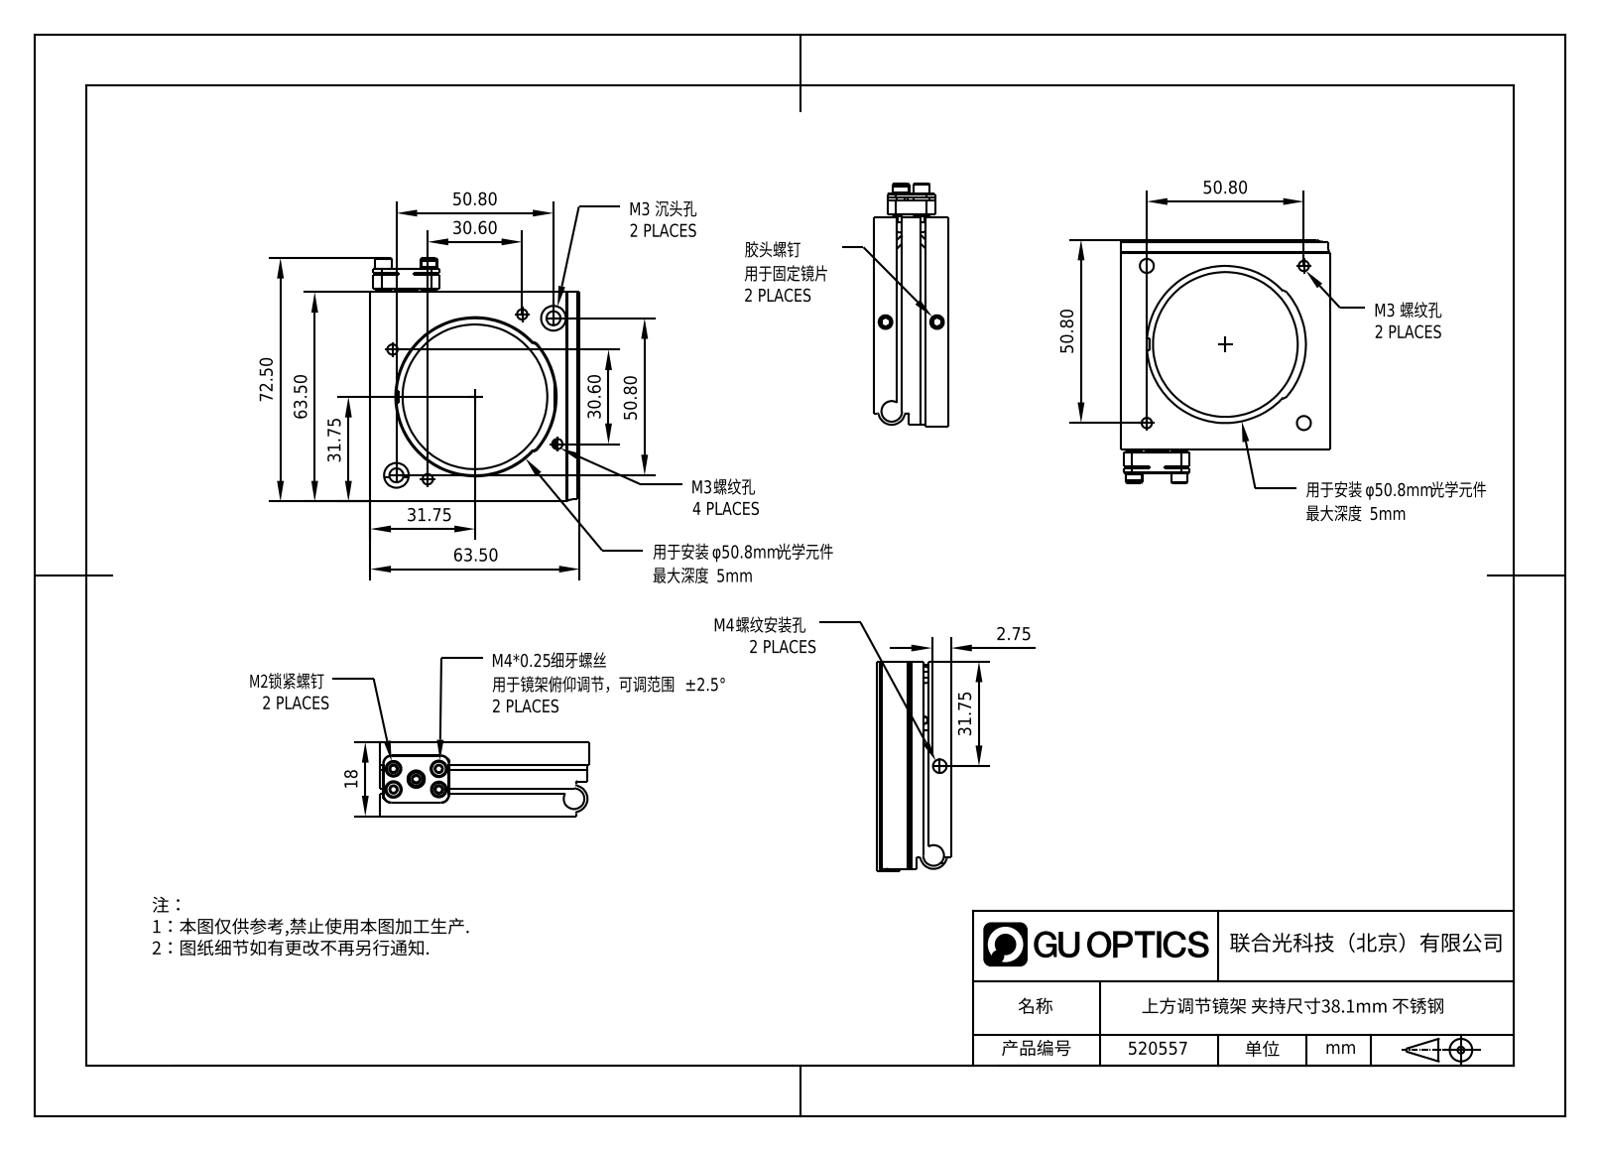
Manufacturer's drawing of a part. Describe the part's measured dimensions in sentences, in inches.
Its 3-D file was written by "SolidWorks 2021 (CONFIG_CONTROL_DESIGN)". It is 0 solids with 252 faces: 80 planar, 118 cylindrical and 54 other. Overall it measures 2.805 by 2.5 by 0.709 inches. Round holes: 6 of diameter 0.098, 5 of diameter 0.13, 2 of diameter 0.134, 2 of diameter 0.197, 2 of diameter 0.236, 1 of diameter 0.059, 1 of diameter 0.157, 1 of diameter 1.882. Round bosses or shafts: 2 of diameter 0.157, 2 of diameter 0.15, 1 of diameter 0.118, 1 of diameter 0.059. Partial cylindrical surfaces (rounded edges, fillets, slot ends): 6 of radius 0.014, 4 of radius 0.059, 4 of radius 0.079, 2 of radius 0.03, 2 of radius 0.039, 2 of radius 0.089, 2 of radius 0.098, 2 of radius 0.128. The main face-to-face distances are 0.226, 0.049, 0.266, 0.443, 0.217, 0.492, 0.177, 0.276, 0.709, 0.02. The hole center spacings are 0.402, 1.21, 1.414, 1.602, 1.711, 2, 2.088, 2.601.
